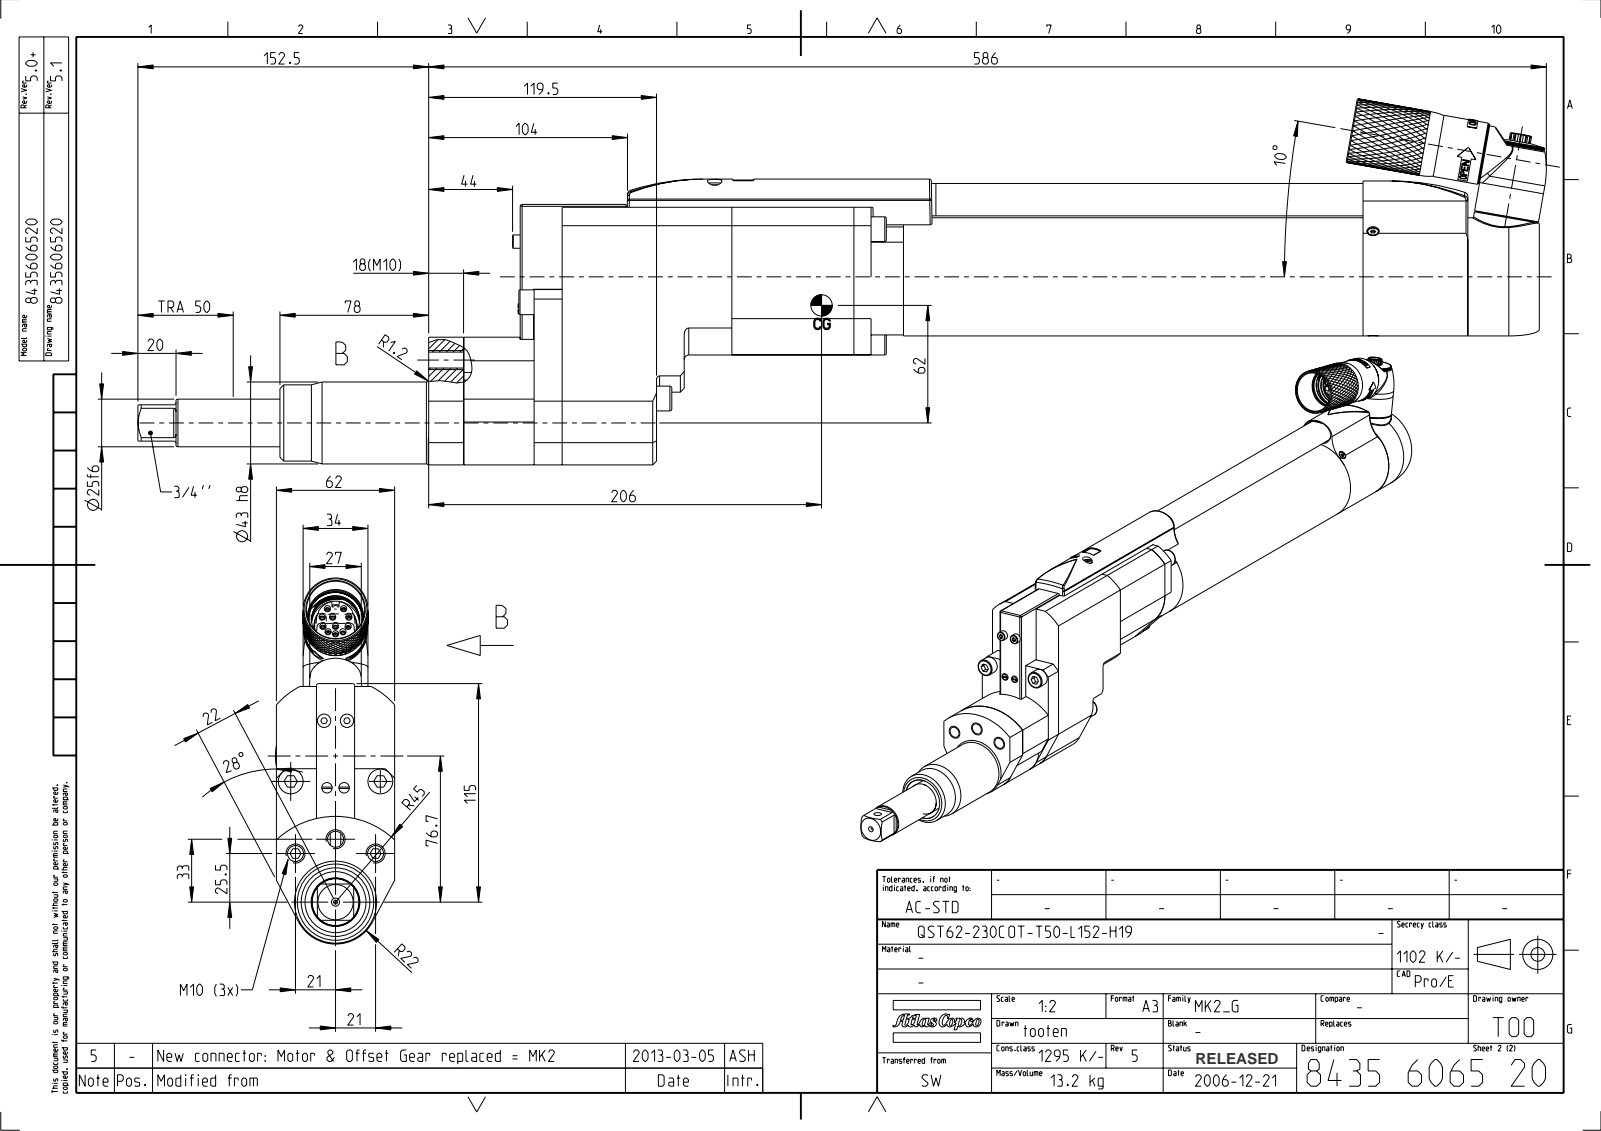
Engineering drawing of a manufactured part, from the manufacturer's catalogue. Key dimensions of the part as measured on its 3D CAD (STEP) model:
Part name (STEP PRODUCT): EXT_COMP_SW0010_1_1; EXT_COMP_SW0010_1_2; EXT_COMP_SW0010_1_ASM; PRT0045 (+3 more)
STEP written by: CREO PARAMETRIC BY PTC INC, 2020281 (CONFIG_CONTROL_DESIGN)
Units: inches
Bodies: 5 solids, 1617 faces (727 planar, 416 cylindrical, 474 other)
Overall size (bounding box): 29.08 × 7.561 × 2.461
Volume: 154.9 in³ · Surface area: 410.5 in²
Round holes (diameter × count): ⌀0.13 ×9, ⌀0.128 ×4, ⌀0.433 ×4, ⌀0.256 ×3, ⌀0.33 ×3, ⌀0.097 ×2, ⌀0.138 ×2, ⌀0.194 ×2, ⌀0.252 ×2, ⌀0.262 ×2, ⌀1.122 ×2, ⌀1.126 ×2
Round bosses / shafts (diameter × count): ⌀0.512 ×7, ⌀0.276 ×4, ⌀1.339 ×3, ⌀0.118 ×3, ⌀0.22 ×2, ⌀2.441 ×1, ⌀2.283 ×1, ⌀2.205 ×1
Partial cylindrical surfaces — rounded edges, fillets, slot ends (radius × count): R0.011 ×12, R0.02 ×12, R0.039 ×12, R0.008 ×4, R0.02 ×4, R0.047 ×4, R0.207 ×4, R0.906 ×4
Main face-to-face distances: 2.441, 2.164, 0.827, 1.614, 1.476, 0.748, 1.416, 1.654, 2.892, 3.64
Hole centre spacings: 1.85, 0.183, 0.472, 0.508, 0.509, 0.878, 1.054, 1.054
